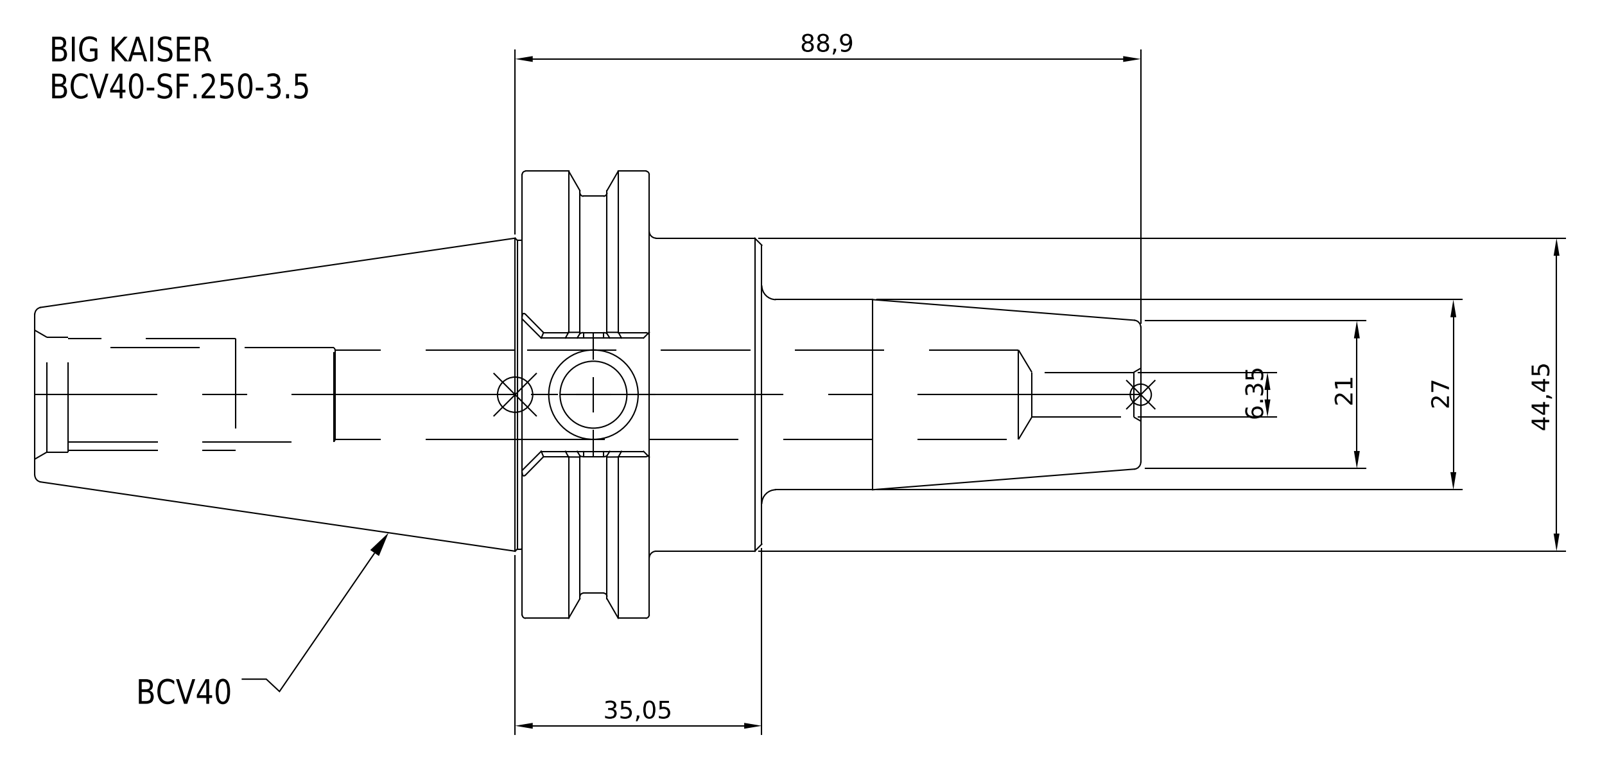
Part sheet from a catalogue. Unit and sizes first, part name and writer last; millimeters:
Units: millimetres
Overall size (bounding box): 157.15 × 63.5 × 63.5
Round holes (diameter × count): ⌀6.35 ×1
Round bosses / shafts (diameter × count): ⌀63.5 ×1, ⌀56.36 ×1, ⌀44.45 ×1, ⌀27 ×1
Main face-to-face distances: 18.05, 16, 34.05, 103.3, 87.3, 69.25, 53.85, 69.85, 87.9, 157.15
Volume: 171 301 mm³ · Surface area: 23 918 mm²
Bodies: 1 solid, 30 faces (8 planar, 14 cylindrical, 8 other)
Part name (STEP PRODUCT): BCV40-SF_250-3_5
STEP written by: SolidWorks 2021 (CONFIG_CONTROL_DESIGN)
